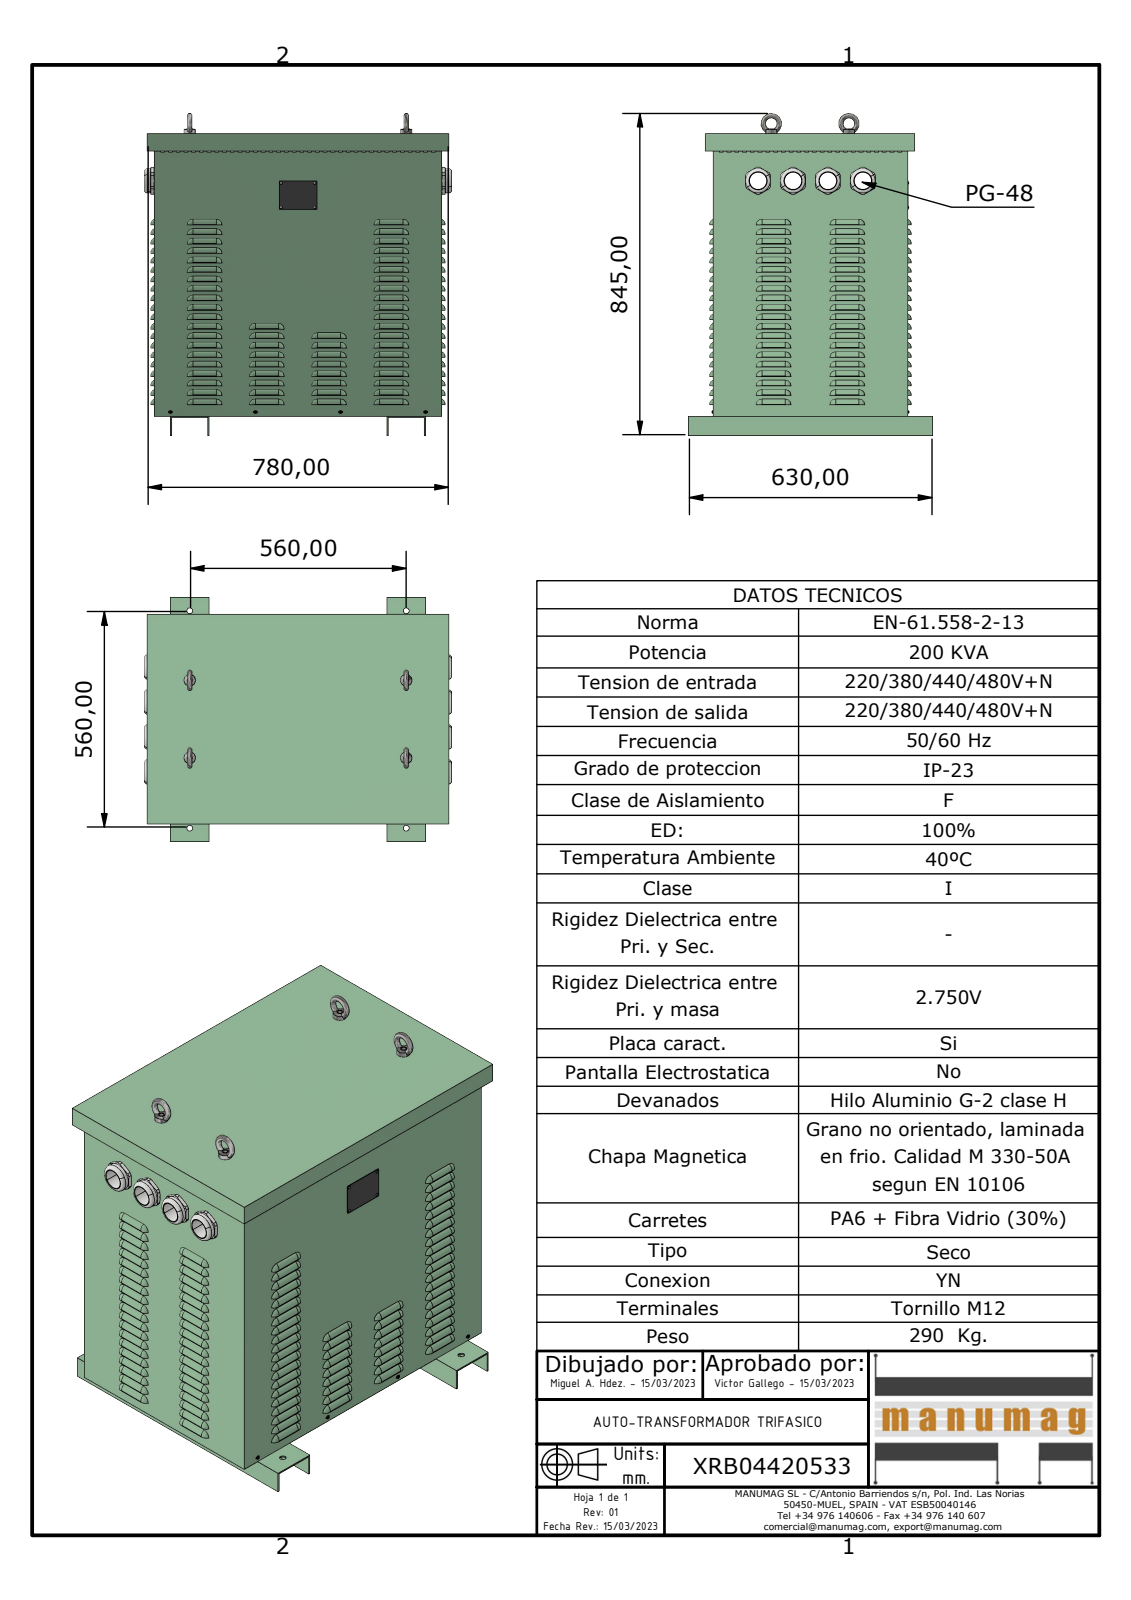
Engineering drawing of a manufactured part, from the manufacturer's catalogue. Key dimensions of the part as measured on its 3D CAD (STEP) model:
Part name (STEP PRODUCT): XRB04420533; JE200 CUERPO; JE160 EXPORT JE200 EXPORT NACIONAL BASE; JE160 EXPORT JE200 EXPORT NACIONAL PATA (+6 more)
STEP written by: Autodesk Inventor 2023 (AUTOMOTIVE_DESIGN)
Units: millimetres
Bodies: 30 solids, 4663 faces (1571 planar, 1992 cylindrical, 1100 other)
Overall size (bounding box): 835 × 795.27 × 630
Volume: 7 588 000 mm³ · Surface area: 6 374 000 mm²
Round holes (diameter × count): ⌀11 ×936, ⌀15 ×12, ⌀4 ×4, ⌀5 ×4, ⌀10.11 ×4, ⌀44 ×4, ⌀60 ×4
Round bosses / shafts (diameter × count): ⌀63 ×4, ⌀59.3 ×4, ⌀59.15 ×4, ⌀57.63 ×4, ⌀30 ×4, ⌀4 ×4, ⌀3.62 ×4, ⌀3.2 ×4
Partial cylindrical surfaces — rounded edges, fillets, slot ends (radius × count): R14 ×194, R7 ×80, R15 ×80, R2.5 ×8, R2 ×4, R35 ×4
Main face-to-face distances: 2, 500, 730, 742, 498, 502, 732, 740, 728, 744
Hole centre spacings: 15, 30, 33.54, 204.55, 159.71, 204, 129.87, 159
